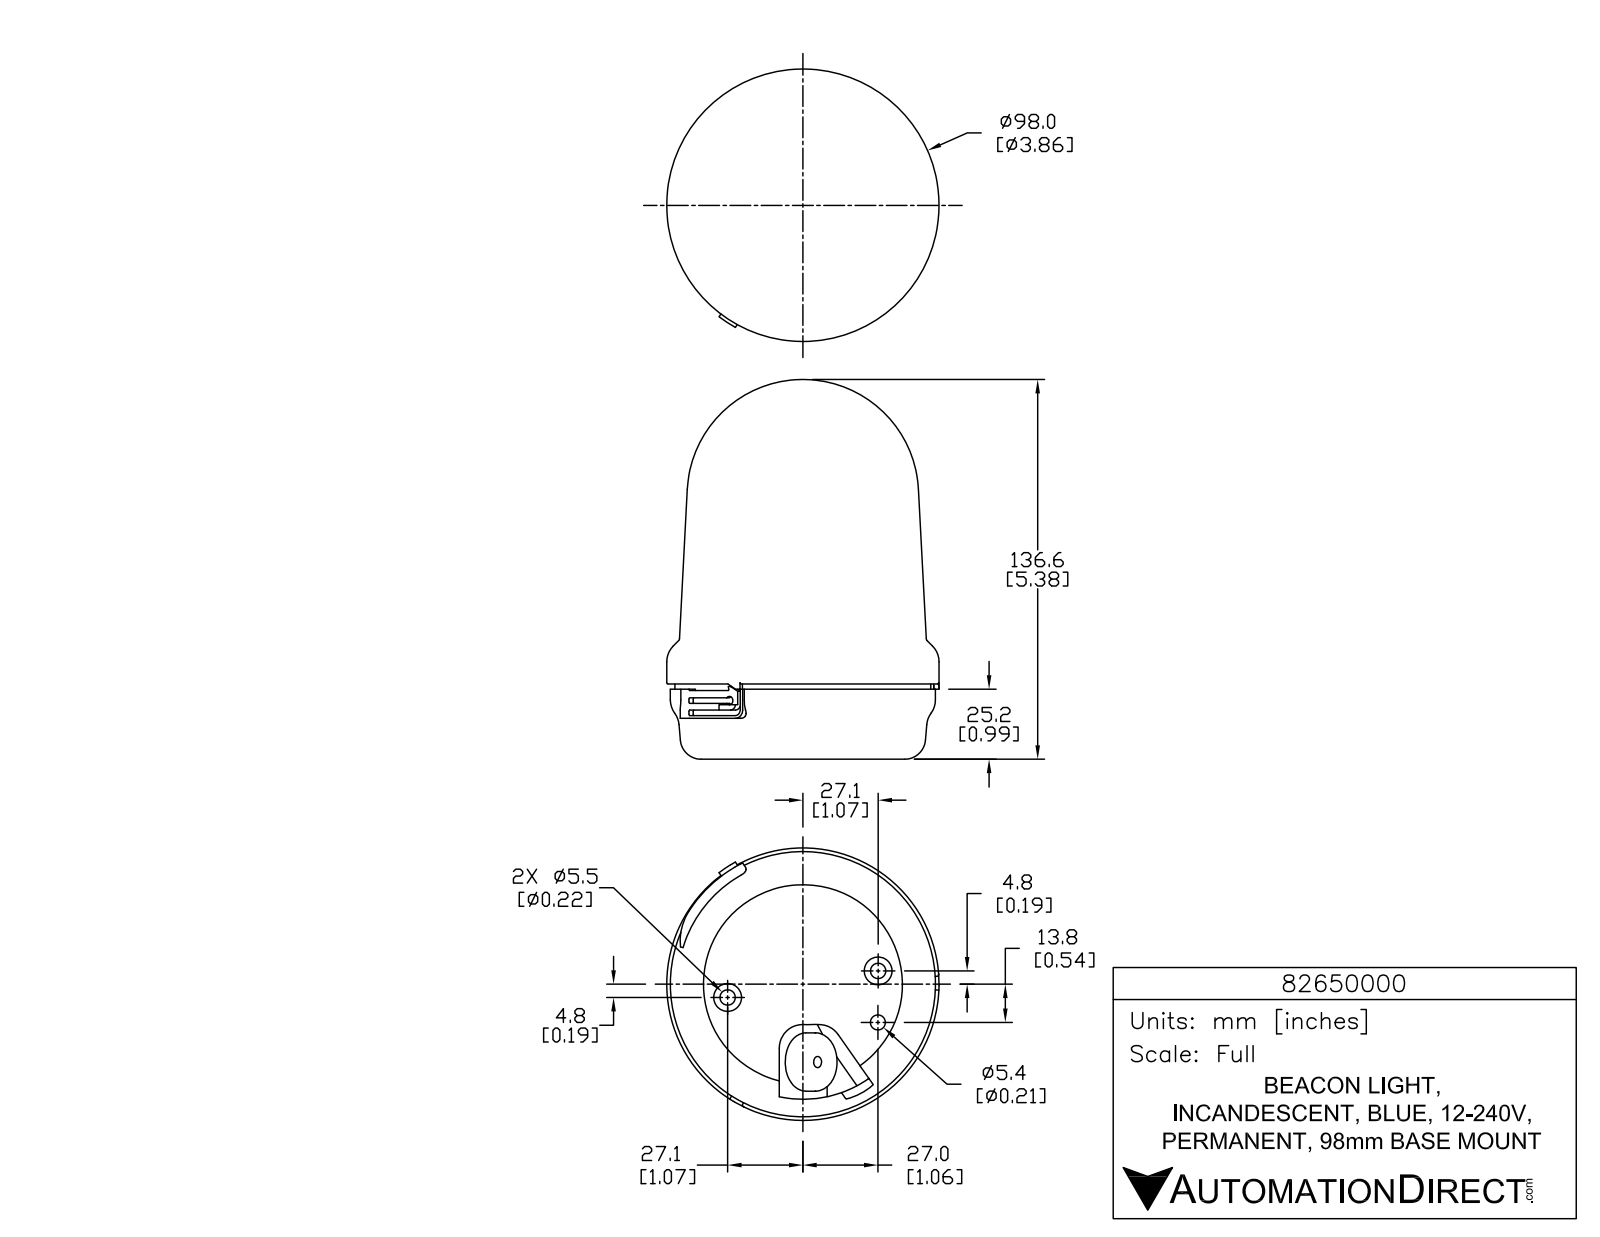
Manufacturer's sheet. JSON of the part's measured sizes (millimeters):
{"part_name": "82650000", "step_written_by": "SolidWorks 2015 (AUTOMOTIVE_DESIGN)", "units": "millimeters", "bodies": {"solids": 1, "faces": 872, "planar": 566, "cylindrical": 204, "other": 102}, "overall_size": [136.6, 98, 98], "volume_mm3": 732300, "surface_area_mm2": 47520, "round_holes": [[1.5, 3], [5.5, 2], [4, 1], [5.4, 1], [71.6, 1]], "round_bosses_or_shafts": [[8.6, 3], [2.1, 3], [10, 2], [98, 1], [95.4, 1], [92.1, 1], [21, 1]], "partial_cylinders_radius": [[0.1, 9], [0.1, 6], [0.3, 6], [0.3, 6], [0.3, 6], [5, 6], [0.5, 5], [1, 4]], "face_to_face_distances": [26.5, 24.7, 1.9, 0.5, 25.2, 27.1, 6, 14.7, 14.2, 10.5], "hole_center_spacings": [27.5, 18.5, 30.3, 54.8, 55]}
